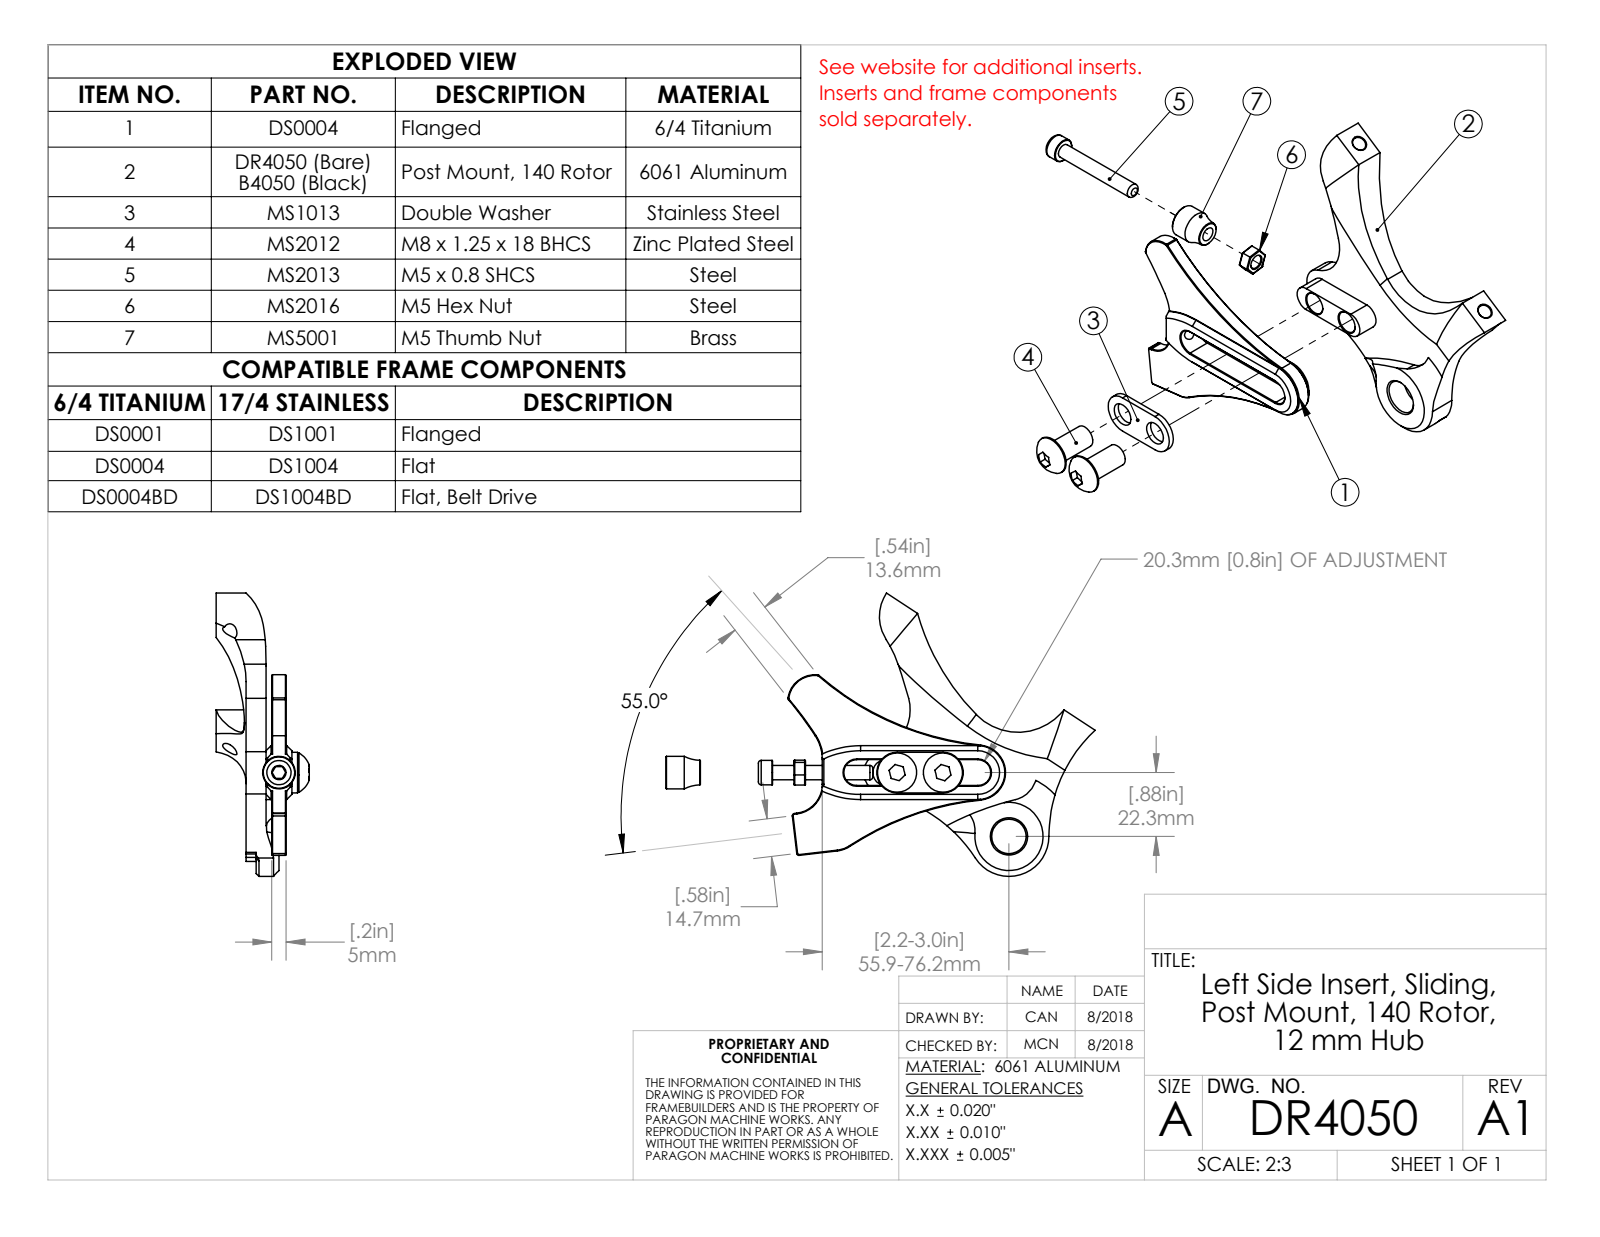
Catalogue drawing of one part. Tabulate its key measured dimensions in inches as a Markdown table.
| quantity | value |
| --- | --- |
| part name | DS0004; MS2012; MS2013; MS1013 (+4 more) |
| STEP written by | SolidWorks 2015 (AUTOMOTIVE_DESIGN) |
| units | inches |
| bodies | 8 solids, 283 faces (87 planar, 103 cylindrical, 93 other) |
| overall size | 5.631 × 3.894 × 1.281 |
| volume | 2.623 in³ |
| surface area | 33.92 in² |
| round holes (diameter × count) | 0.197 × 3, 0.312 × 2, 0.327 × 2, 0.335 × 1, 0.474 × 1 |
| round bosses / shafts (diameter × count) | 0.539 × 2, 0.315 × 2, 0.449 × 1 |
| partial cylindrical surfaces (radius × count) | 0.01 × 12, 0.03 × 4, 0.178 × 4, 0.6 × 3, 0.049 × 2, 0.28 × 2, 0.4 × 2, 1.27 × 2 |
| main face-to-face distances | 0.079, 0.276, 0.274, 0.197, 0.55, 0.353, 0.354, 0.628, 0.356, 0.157 |
| hole center spacings | 0.63, 1.262, 1.77, 2.921 |
